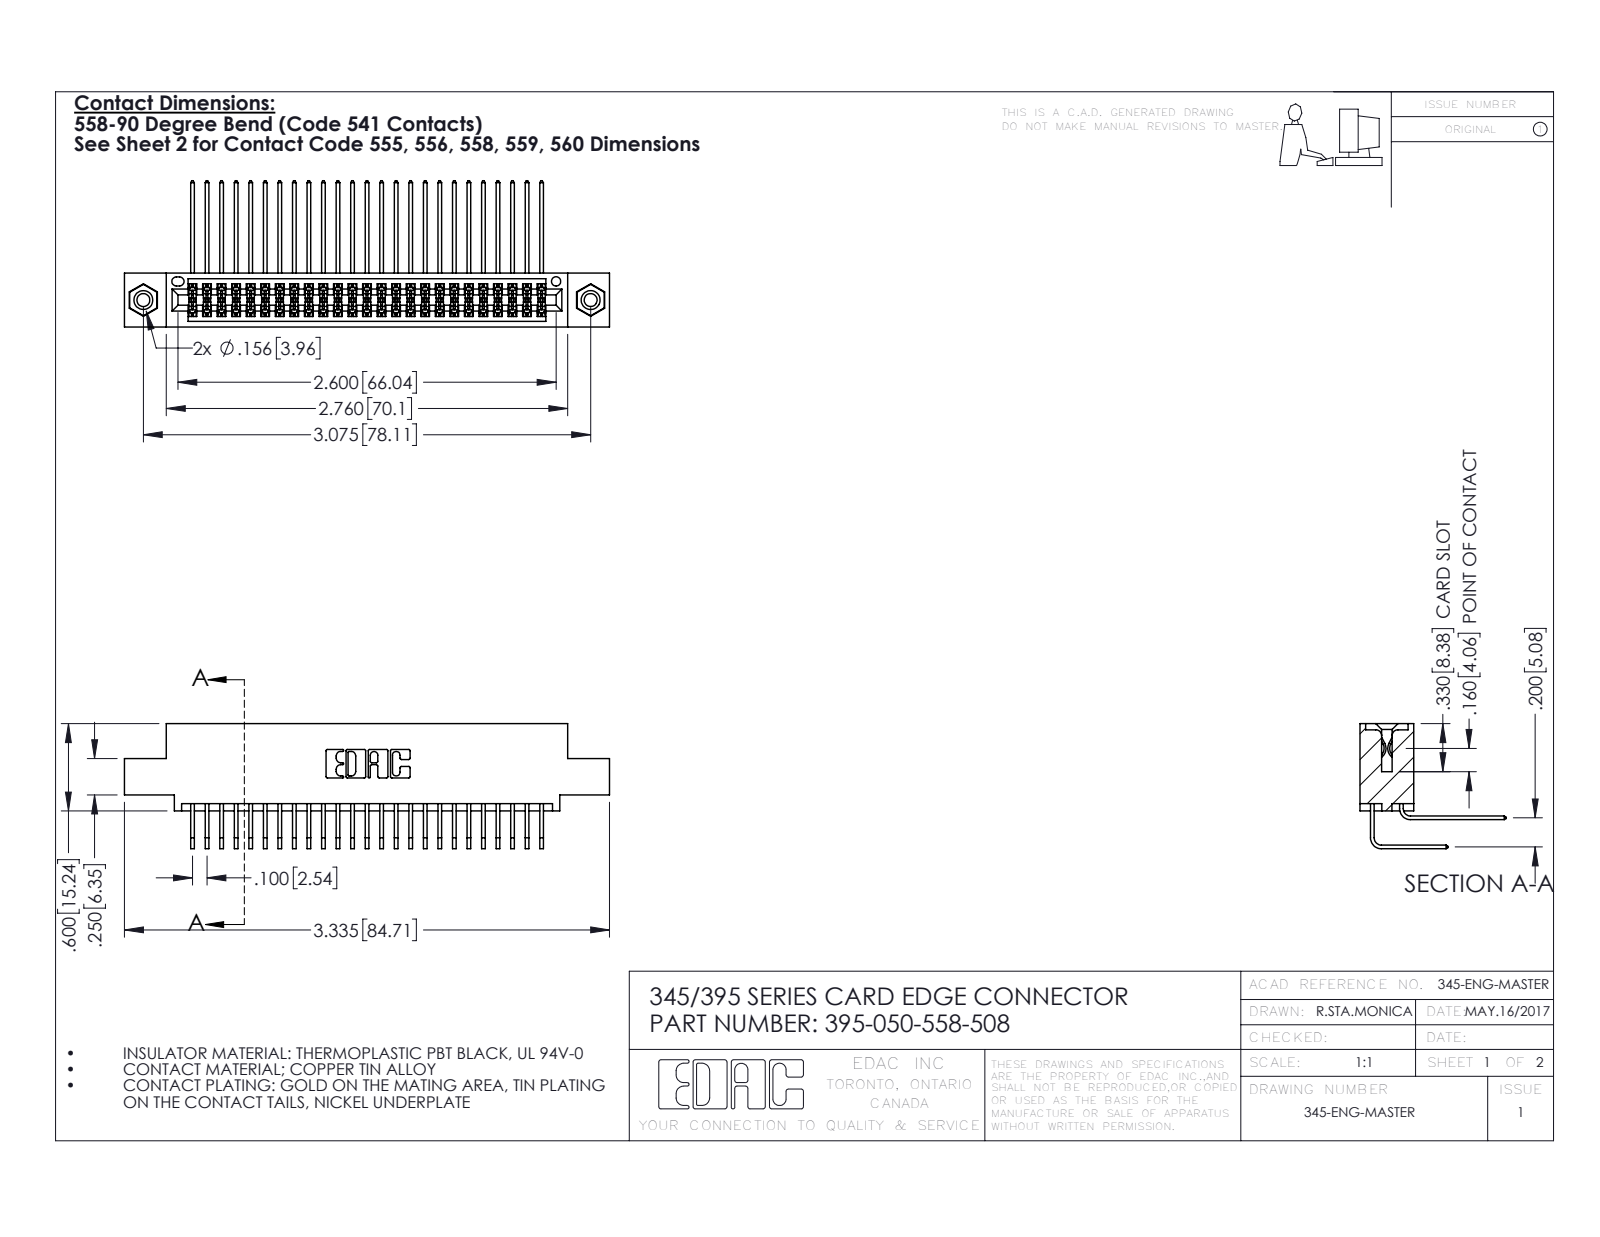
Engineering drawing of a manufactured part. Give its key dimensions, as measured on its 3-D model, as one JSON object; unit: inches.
{"part_name": "345-292-001_558 559 Tail - 1; 395-050-558-508; 345-292-001_558 Tail - 2; 345 Part_0.110 Offset - 0.156 Dia-TI (+1 more)", "step_written_by": "SolidWorks 2016 (CONFIG_CONTROL_DESIGN)", "units": "inches", "bodies": {"solids": 53, "faces": 2790, "planar": 1866, "cylindrical": 908, "other": 16}, "overall_size": [3.335, 1.005, 0.859], "volume_in3": 0.505, "surface_area_in2": 20.73, "round_holes": [[0.089, 2], [0.125, 2], [0.156, 2], [0.064, 1]], "round_bosses_or_shafts": [[0.155, 2]], "partial_cylinders_radius": [[0.006, 76], [0.01, 22], [0.007, 6], [0.031, 6], [0.026, 3], [0.014, 2], [0.019, 2], [0.022, 2]], "face_to_face_distances": [0.072, 0.298, 0.2, 0.37, 0.098, 0.272, 0.025, 0.225, 0.025, 0.175], "hole_center_spacings": [0.27, 2.84, 3.075]}
